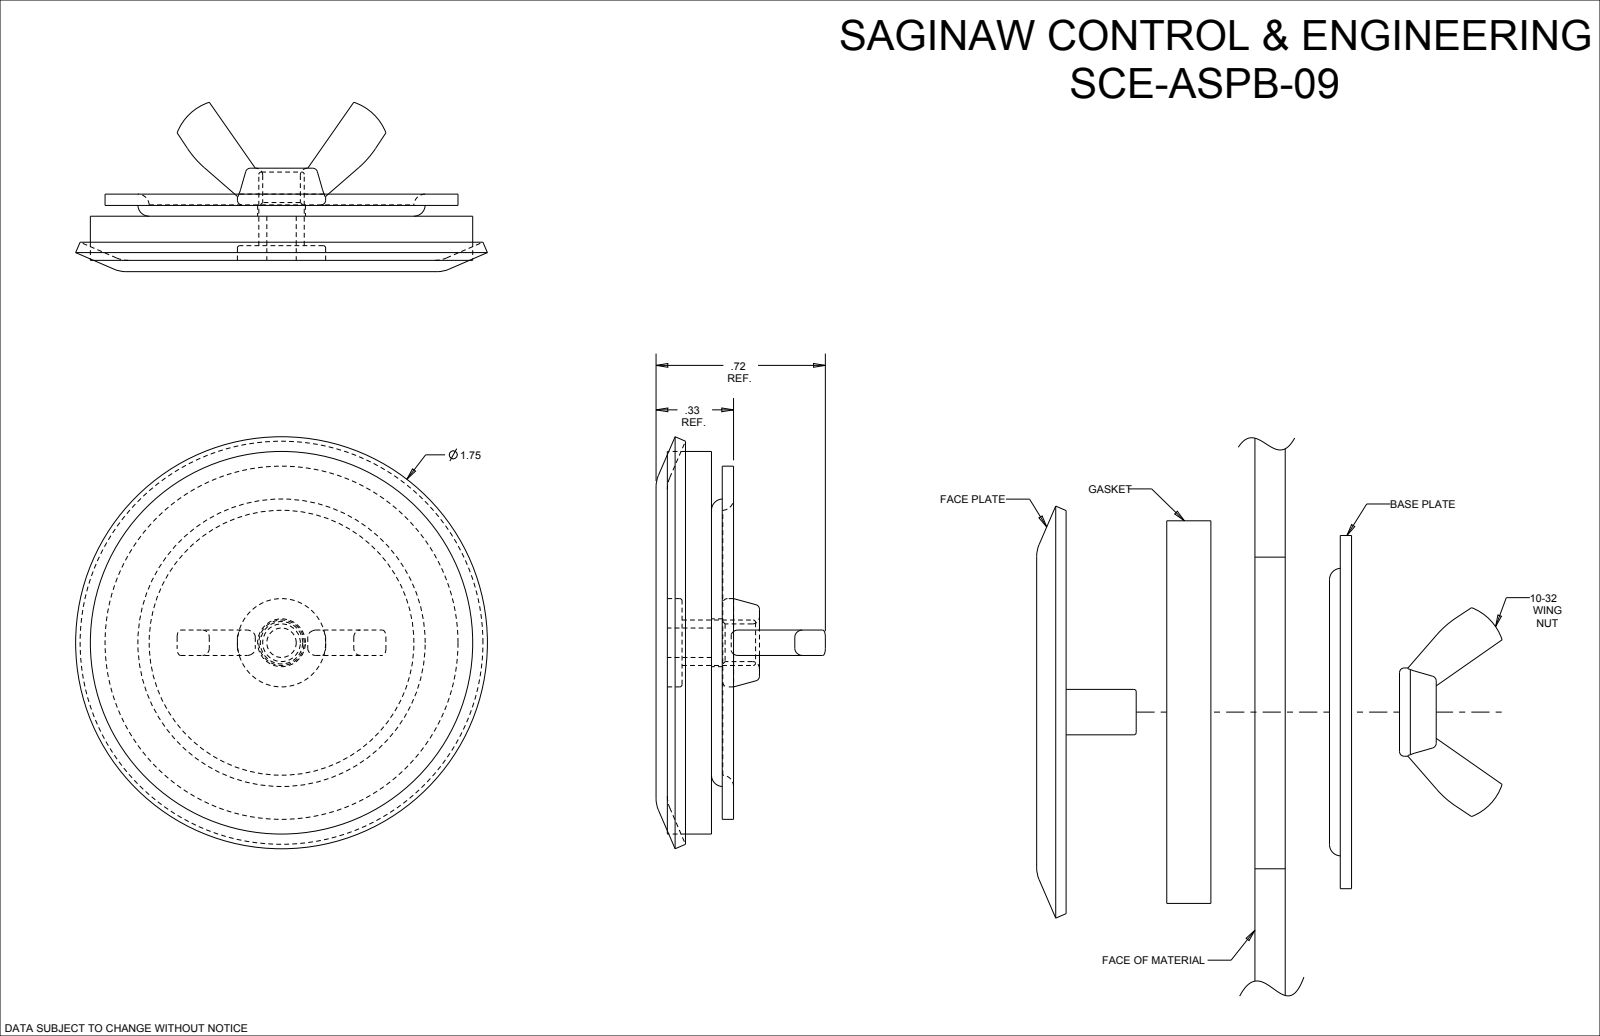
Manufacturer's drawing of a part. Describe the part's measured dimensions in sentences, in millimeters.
The part is named "SCE-ASPB-09". Its 3-D file was written by "SolidWorks 2019 (CONFIG_CONTROL_DESIGN)". It is 5 solids with 71 faces: 27 planar, 24 cylindrical and 20 other. Overall it measures 44.5 by 44.5 by 18.3 millimeters. Its volume is 10 400 cubic millimeters and its surface area 9 948 square millimeters. Round holes: 1 of diameter 3.2, 1 of diameter 4.1, 1 of diameter 5.2. Round bosses or shafts: 1 of diameter 41.3, 1 of diameter 38.1, 1 of diameter 9.5, 1 of diameter 4.9. Partial cylindrical surfaces (rounded edges, fillets, slot ends): 12 of radius 0.8, 2 of radius 5.6, 2 of radius 10.2. The main face-to-face distances are 4.7, 1.2, 6, 1.2, 7.1, 7.2, 2.4, 8.4, 5.9, 2.7.
